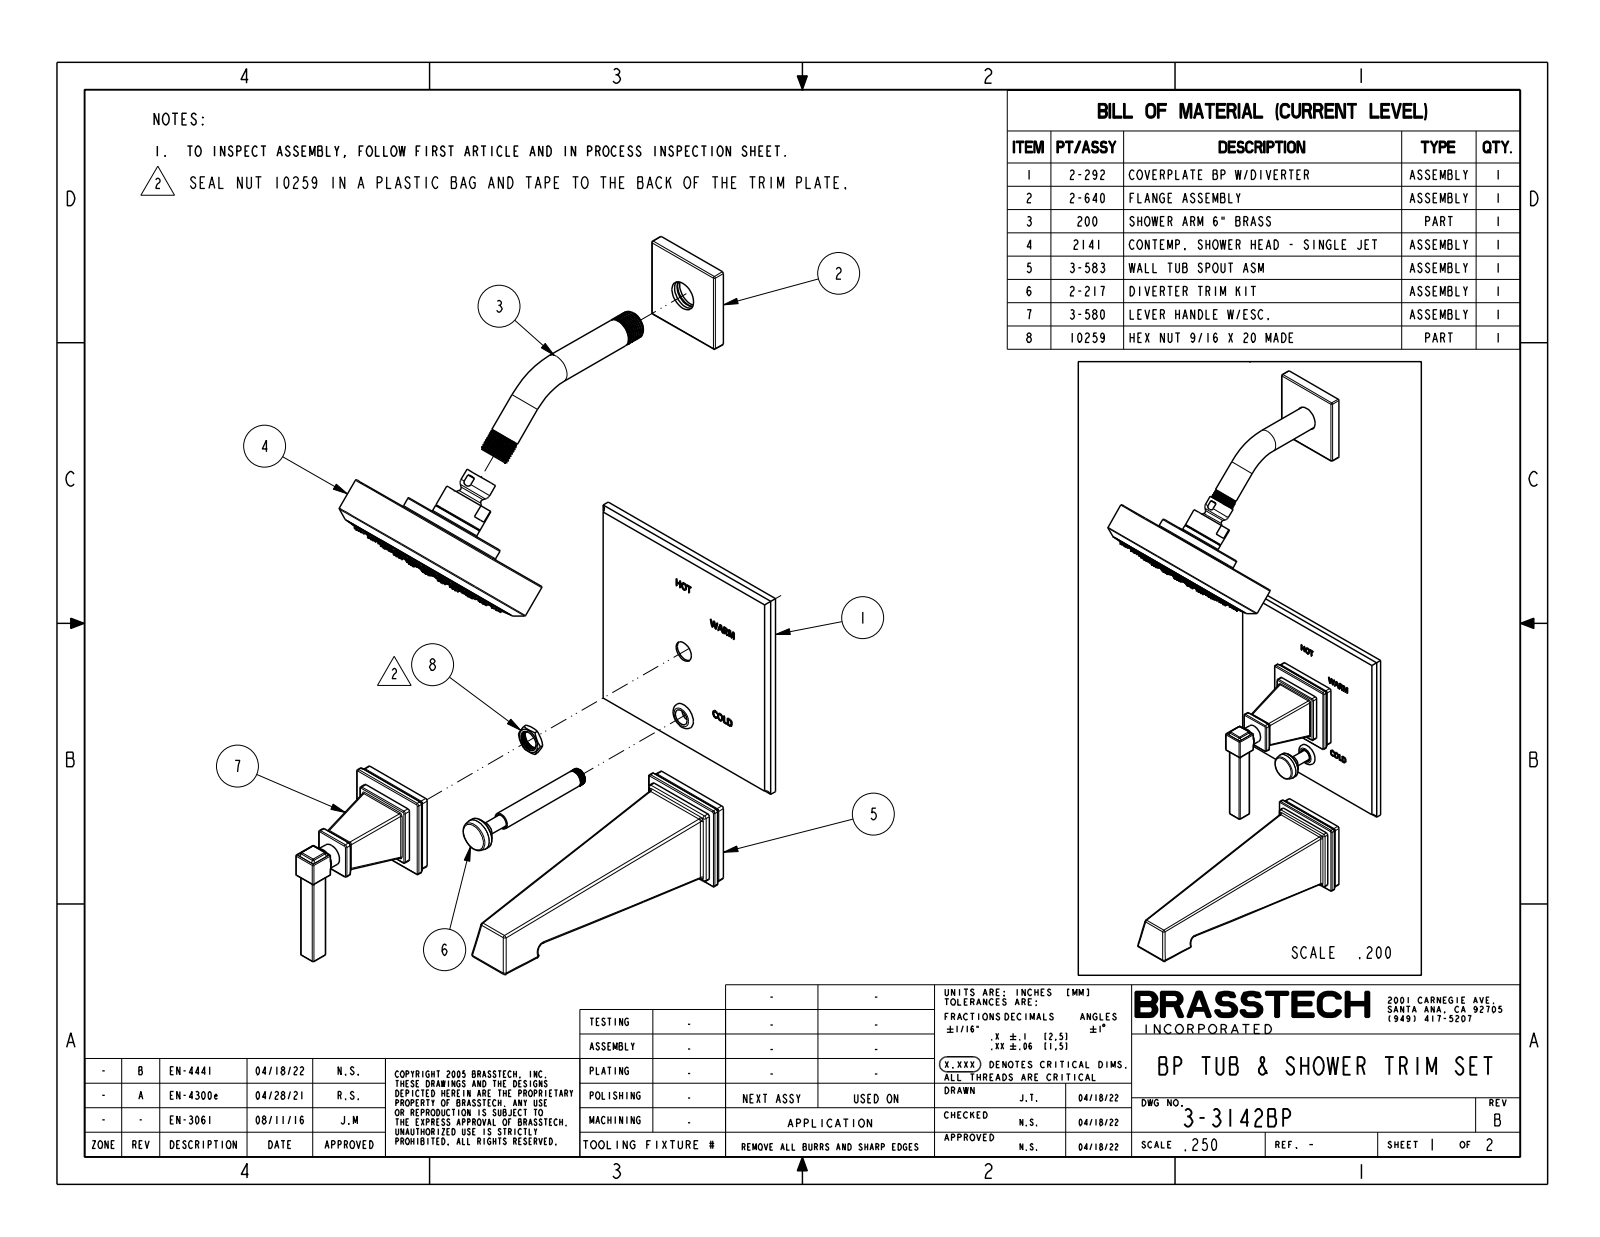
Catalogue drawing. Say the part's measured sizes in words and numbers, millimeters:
The part is named "3-3142BP". Its 3-D file was written by "CREO PARAMETRIC BY PTC INC, 2018400 (CONFIG_CONTROL_DESIGN)". It is 3 solids with 1434 faces: 288 planar, 359 cylindrical and 787 other. Overall it measures 520.7 by 215.5 by 165.1 millimeters. Its volume is 1 284 000 cubic millimeters and its surface area 189 800 square millimeters. Round holes: 90 of diameter 1.3, 1 of diameter 5.6, 1 of diameter 133.5. Round bosses or shafts: 2 of diameter 35.6, 2 of diameter 20.7, 1 of diameter 150.1, 1 of diameter 132.6, 1 of diameter 74.2, 1 of diameter 23, 1 of diameter 22.9, 1 of diameter 19.5. Partial cylindrical surfaces (rounded edges, fillets, slot ends): 56 of radius 0.8, 49 of radius 1.5, 12 of radius 2.3, 8 of radius 1, 4 of radius 3.2, 4 of radius 5.8, 4 of radius 8.1, 1 of radius 5.1. The main face-to-face distances are 8, 10.4, 8.9, 0.9, 7.4, 2.5, 1.5, 10.7, 18.4, 9.5. The hole center spacings are 24.9, 35.8, 10.9, 14, 34.1, 48.1, 14.6, 21.6.
